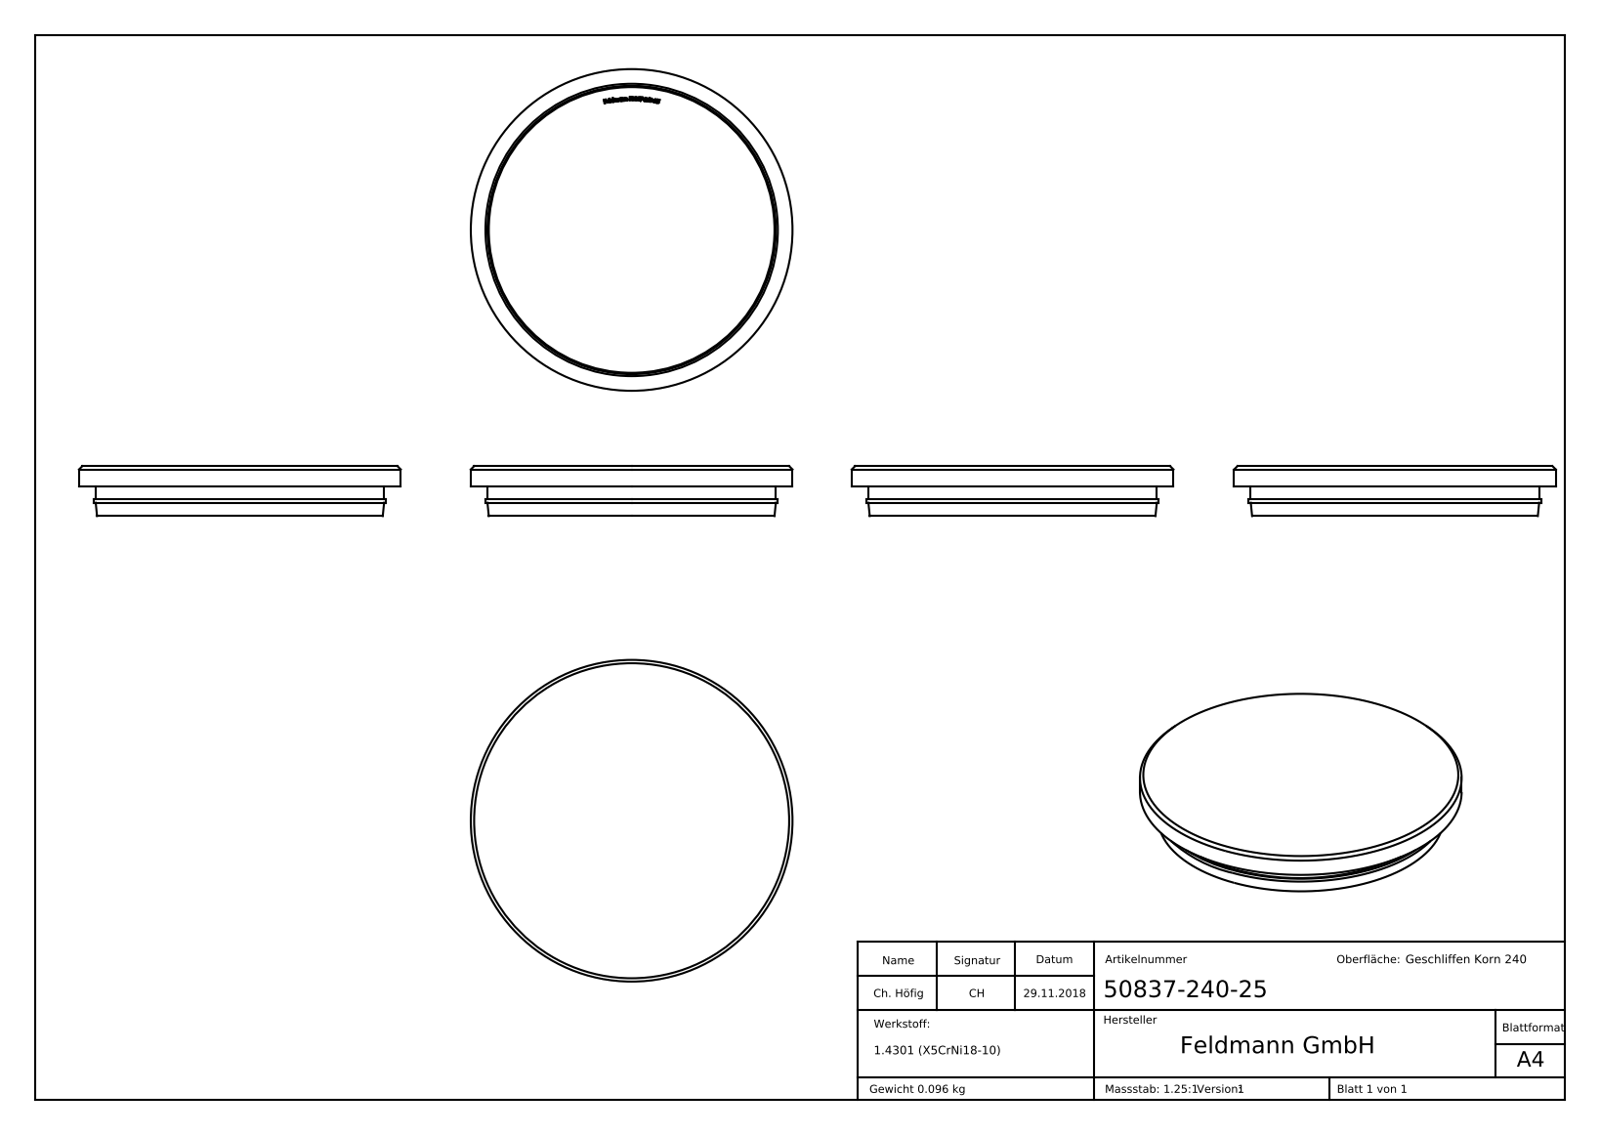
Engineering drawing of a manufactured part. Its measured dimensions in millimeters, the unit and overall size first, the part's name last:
Units: millimetres
Overall size (bounding box): 48.3 × 48.3 × 7.5
Round bosses / shafts (diameter × count): ⌀48.3 ×1, ⌀43.9 ×1, ⌀43.3 ×1
Main face-to-face distances: 7.5, 4.5, 3, 2, 2.5, 0.5, 5.5, 5, 1.5, 4
Volume: 12 097 mm³ · Surface area: 4 766 mm²
Bodies: 1 solid, 276 faces (141 planar, 6 cylindrical, 129 other)
Part name (STEP PRODUCT): 50837-240-25
STEP written by: SolidWorks 2015 (CONFIG_CONTROL_DESIGN)
